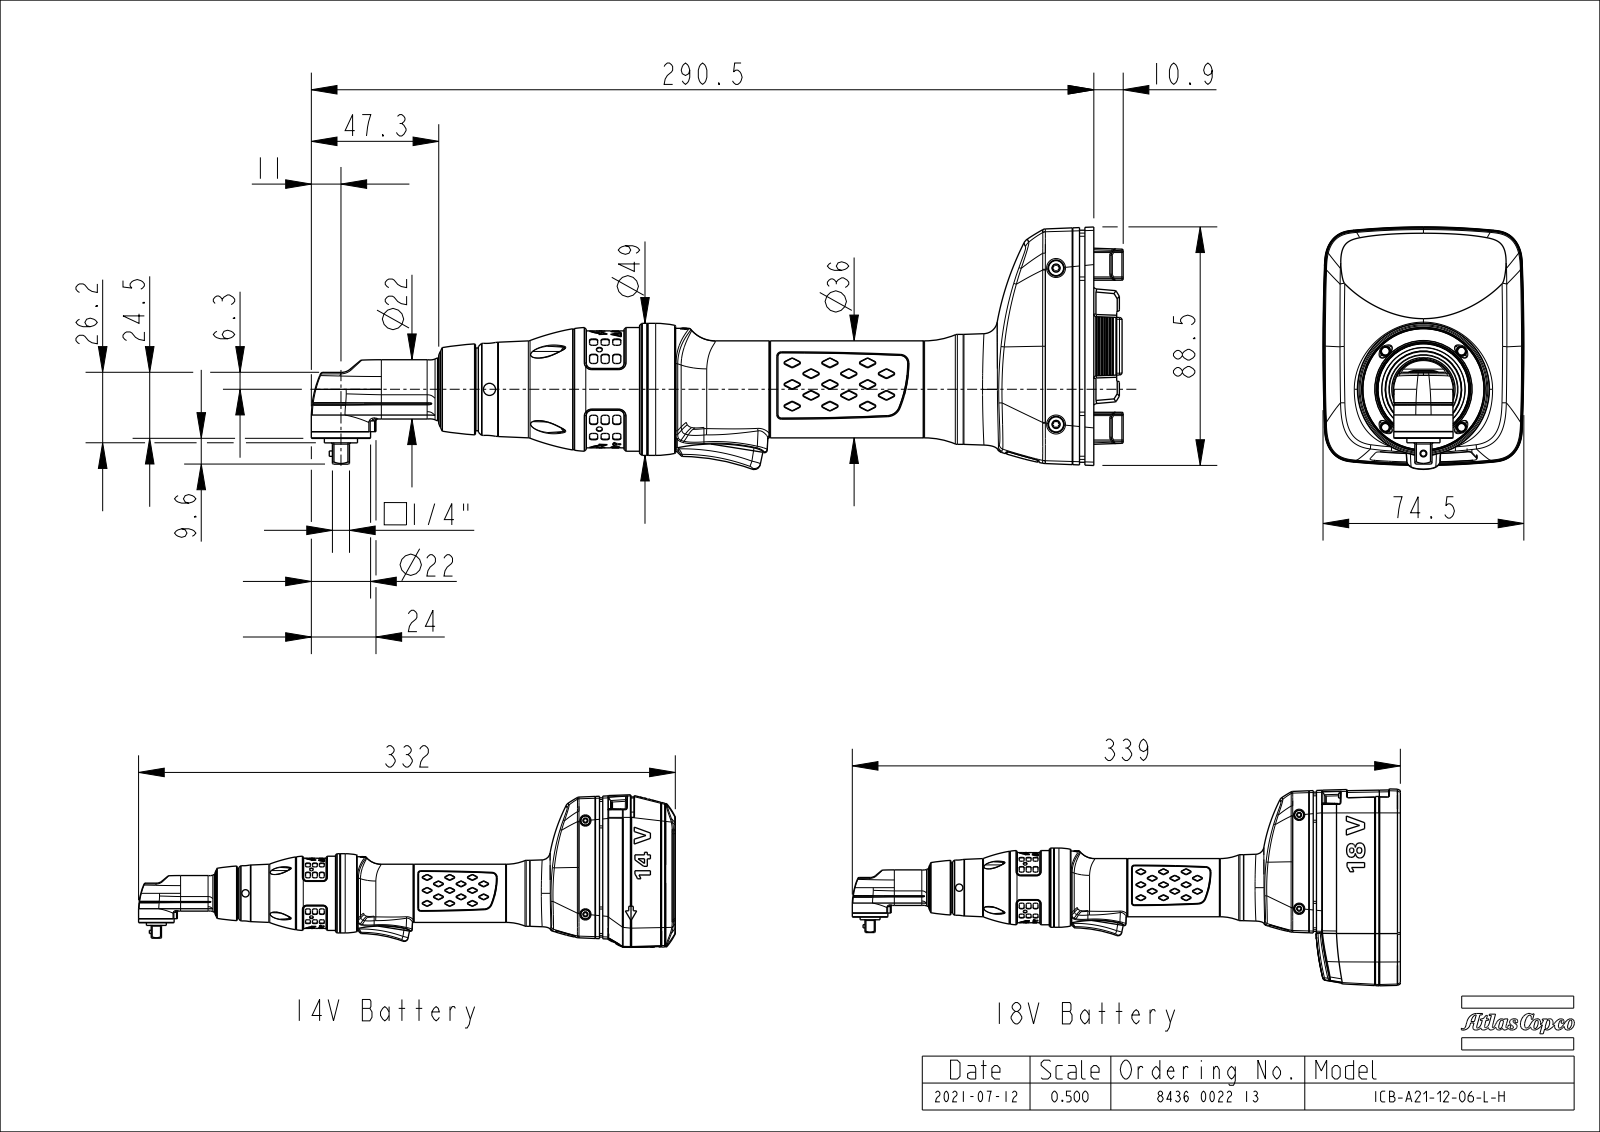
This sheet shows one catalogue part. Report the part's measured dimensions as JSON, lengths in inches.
{"part_name": "EXT_COMP_SW0013", "step_written_by": "CREO PARAMETRIC BY PTC INC, 2020281 (CONFIG_CONTROL_DESIGN)", "units": "inches", "bodies": {"solids": 2, "faces": 3489, "planar": 887, "cylindrical": 1037, "other": 1565}, "overall_size": [11.866, 3.543, 2.935], "volume_in3": 28.61, "surface_area_in2": 106.5, "round_holes": [[0.102, 4], [0.177, 2], [0.236, 2], [0.043, 1], [0.063, 1], [0.098, 1], [0.138, 1], [0.492, 1], [0.565, 1], [0.906, 1]], "round_bosses_or_shafts": [[0.315, 4], [0.866, 2], [0.22, 2], [0.118, 2], [1.929, 1], [1.807, 1], [1.783, 1], [1.606, 1]], "partial_cylinders_radius": [[0.012, 254], [0.02, 159], [0.039, 54], [0.004, 32], [0.011, 24], [0.015, 24], [0.02, 24], [0.027, 24]], "face_to_face_distances": [4.744, 4.743, 0.797, 0.413, 0.079, 0.331, 2.362, 5.156, 5.157, 0.266], "hole_center_spacings": [0.346, 0.49, 0.693, 0.939, 1.825, 2.171, 2.192, 2.206]}
